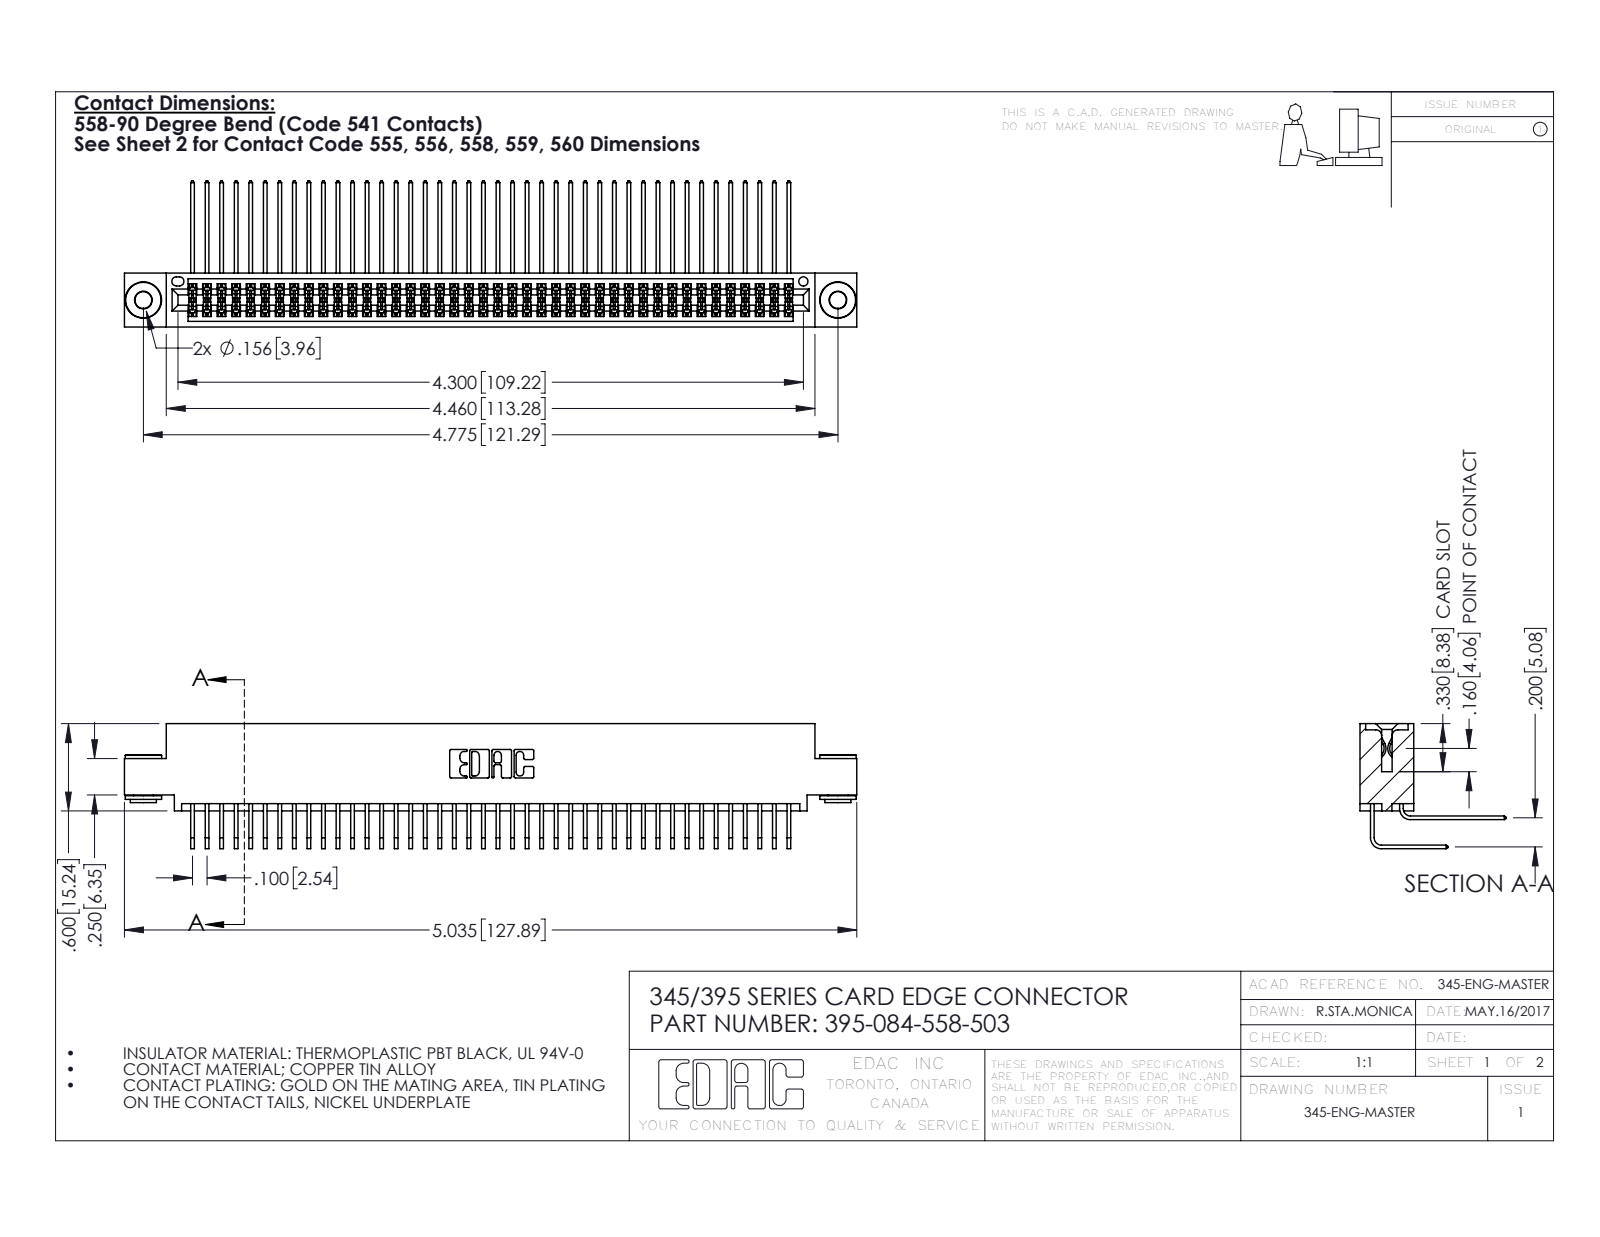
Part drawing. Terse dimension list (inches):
name: 345-292-001_558 559 Tail - 1; 345 Part_0.110 Offset - 0.156 Dia-TH; 395-084-558-503; 345-250-002_345-250-002-102 (+1 more)
written by: SolidWorks 2016 (CONFIG_CONTROL_DESIGN)
unit: in
bodies: 87 solids, 4536 faces (3034 planar, 1494 cylindrical, 8 other)
size: 5.035 × 1.005 × 0.859
volume: 0.784 in³; area: 33.44 in²
holes: 2× ⌀0.116, 2× ⌀0.156, 1× ⌀0.064
bosses: 2× ⌀0.25, 2× ⌀0.18, 2× ⌀0.136
rounds: 127× R0.006, 22× R0.01, 6× R0.007, 6× R0.031, 3× R0.026, 2× R0.014, 2× R0.019, 2× R0.022
face distances: 0.072, 0.298, 0.2, 0.37, 0.025, 0.098, 0.272, 0.225, 0.025, 0.175
hole spacings: 0.27, 4.539, 4.775
